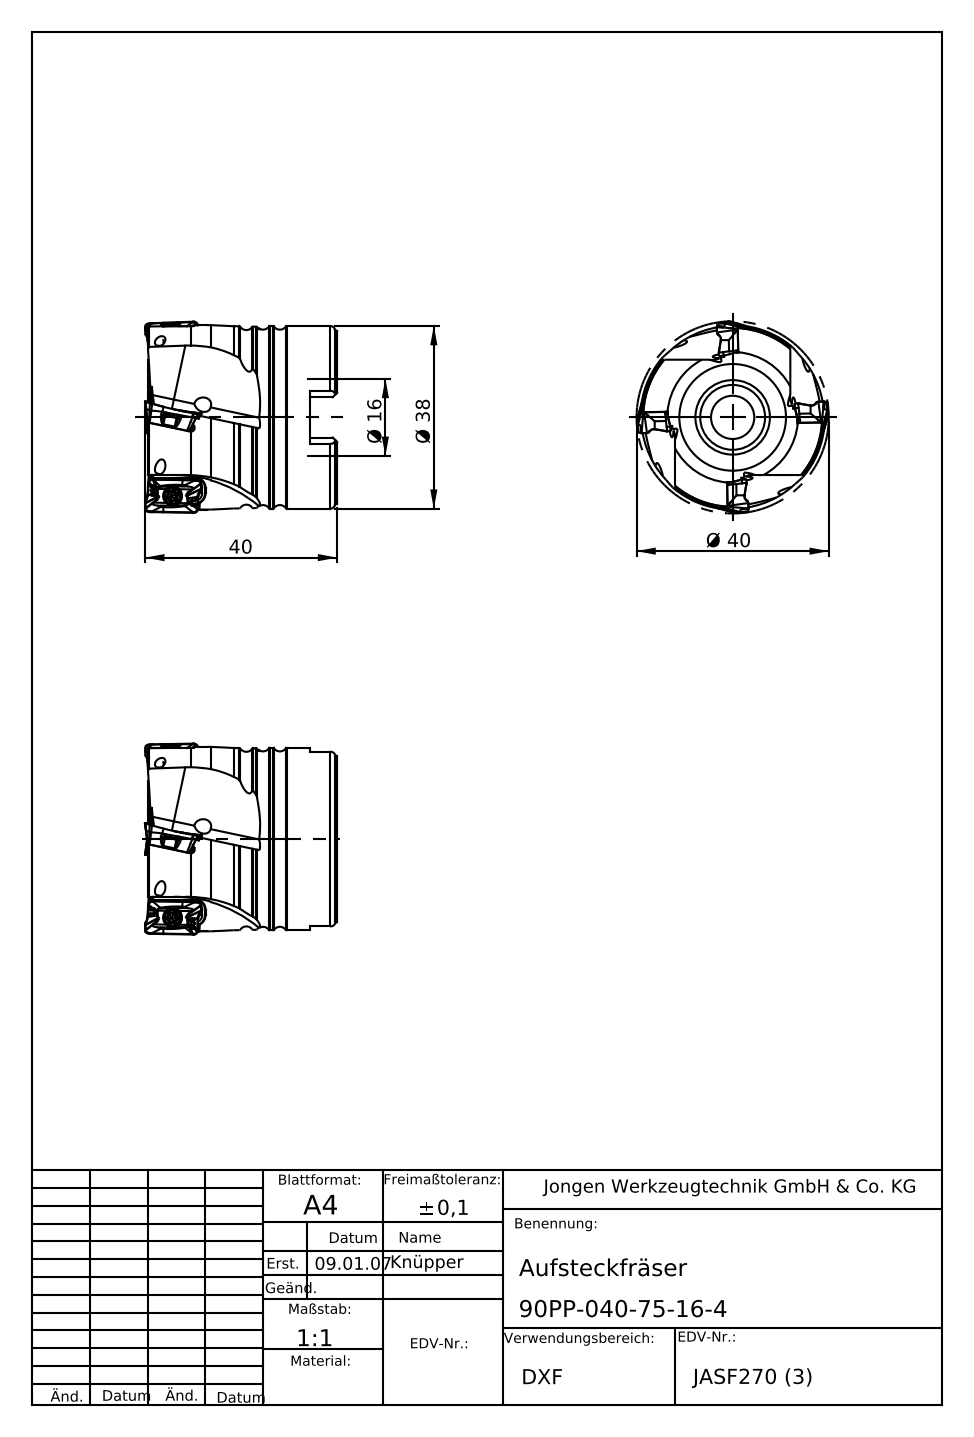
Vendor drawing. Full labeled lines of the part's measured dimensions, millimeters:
Part name (STEP PRODUCT): 90PP-040-75-16-4
STEP written by: SolidWorks 2012 (AUTOMOTIVE_DESIGN)
Units: millimetres
Bodies: 1 solid, 195 faces (63 planar, 63 cylindrical, 69 other)
Overall size (bounding box): 40.05 × 40 × 40
Volume: 34 637 mm³ · Surface area: 9 990 mm²
Round holes (diameter × count): ⌀3 ×4, ⌀9 ×1, ⌀13.5 ×1, ⌀16 ×1, ⌀16.15 ×1, ⌀16.3 ×1
Round bosses / shafts (diameter × count): ⌀38 ×1
Partial cylindrical surfaces — rounded edges, fillets, slot ends (radius × count): R1.5 ×8, R2.1 ×8, R5 ×4, R28.6 ×4, R19.19 ×1
Main face-to-face distances: 38, 5.6, 32.4, 23, 17.4, 15, 8.4, 27.9, 22.3, 4.9
